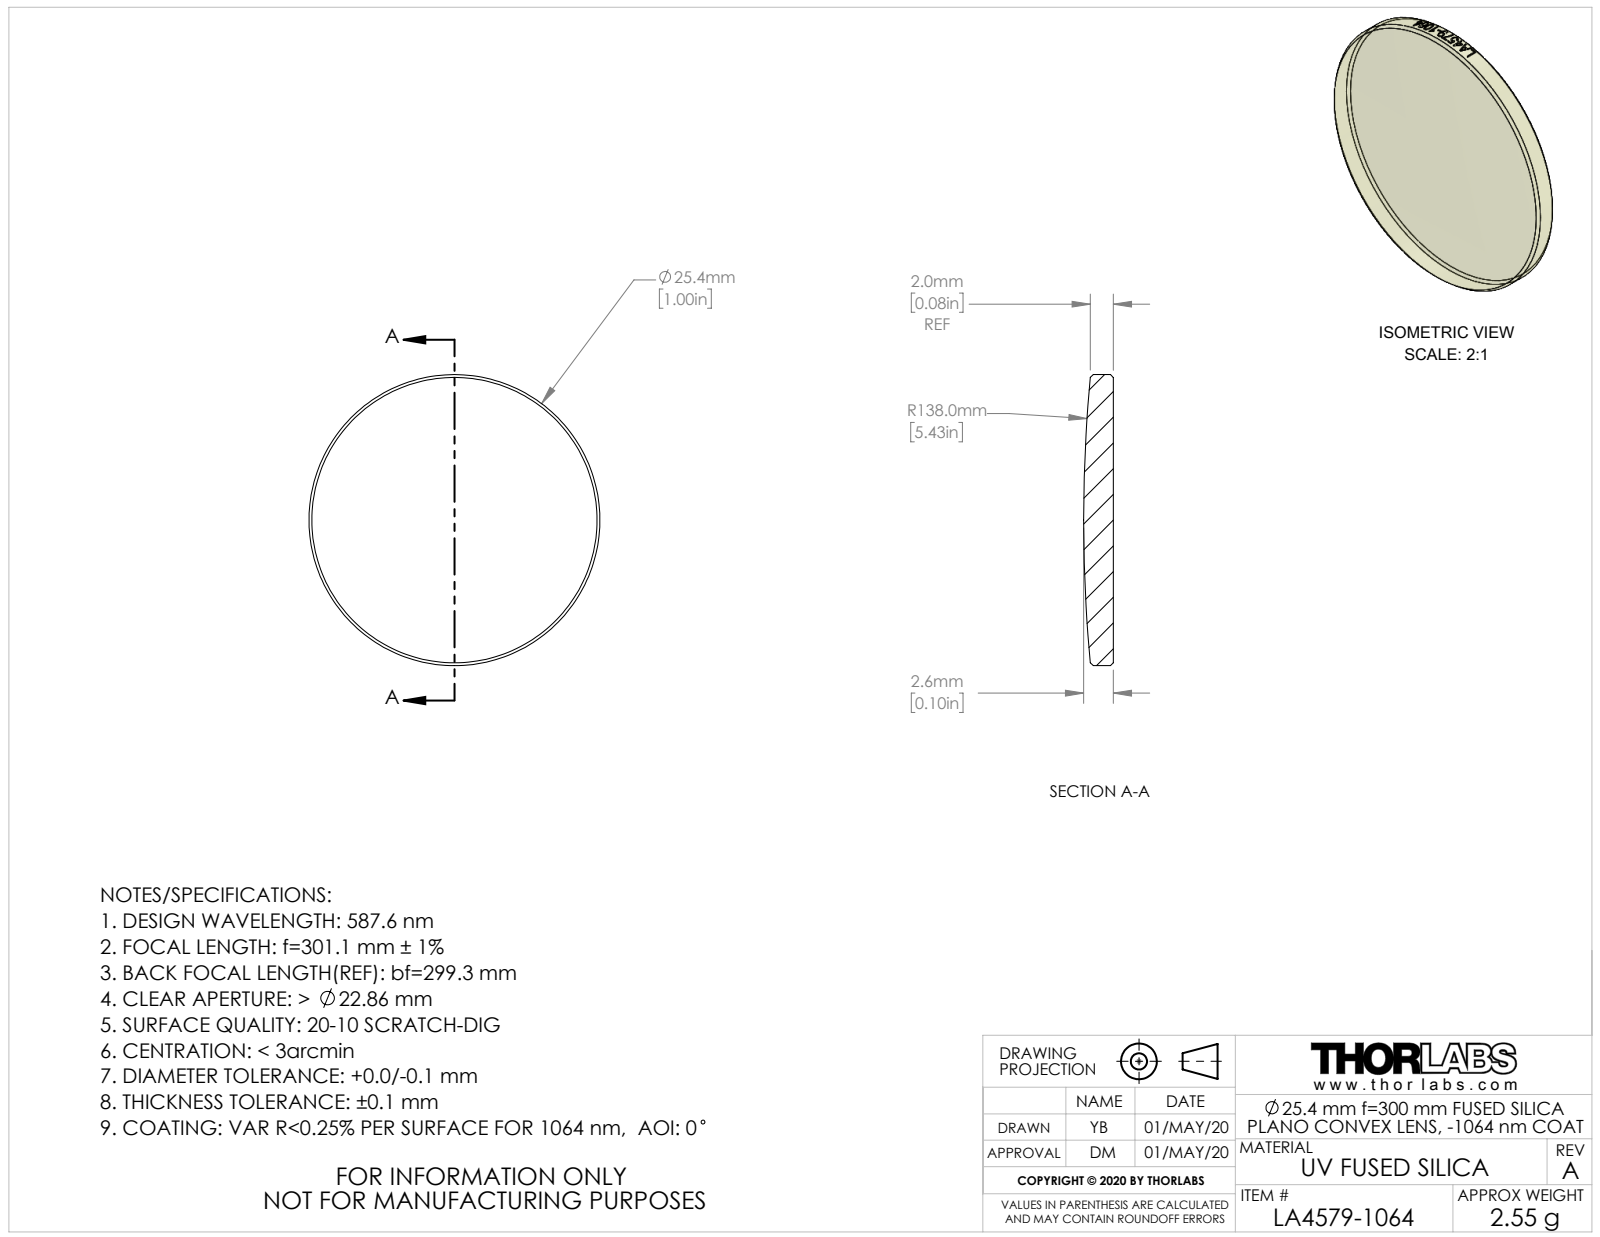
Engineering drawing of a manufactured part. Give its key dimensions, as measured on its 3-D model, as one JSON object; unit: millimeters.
{"part_name": "CTN015549-E0W", "step_written_by": "SolidWorks 2018 (AUTOMOTIVE_DESIGN)", "units": "millimeters", "bodies": {"solids": 1, "faces": 29, "planar": 1, "cylindrical": 22, "other": 6}, "overall_size": [25.4, 25.4, 2.59], "volume_mm3": 1158, "surface_area_mm2": 1152, "round_bosses_or_shafts": [[25.4, 1]]}
